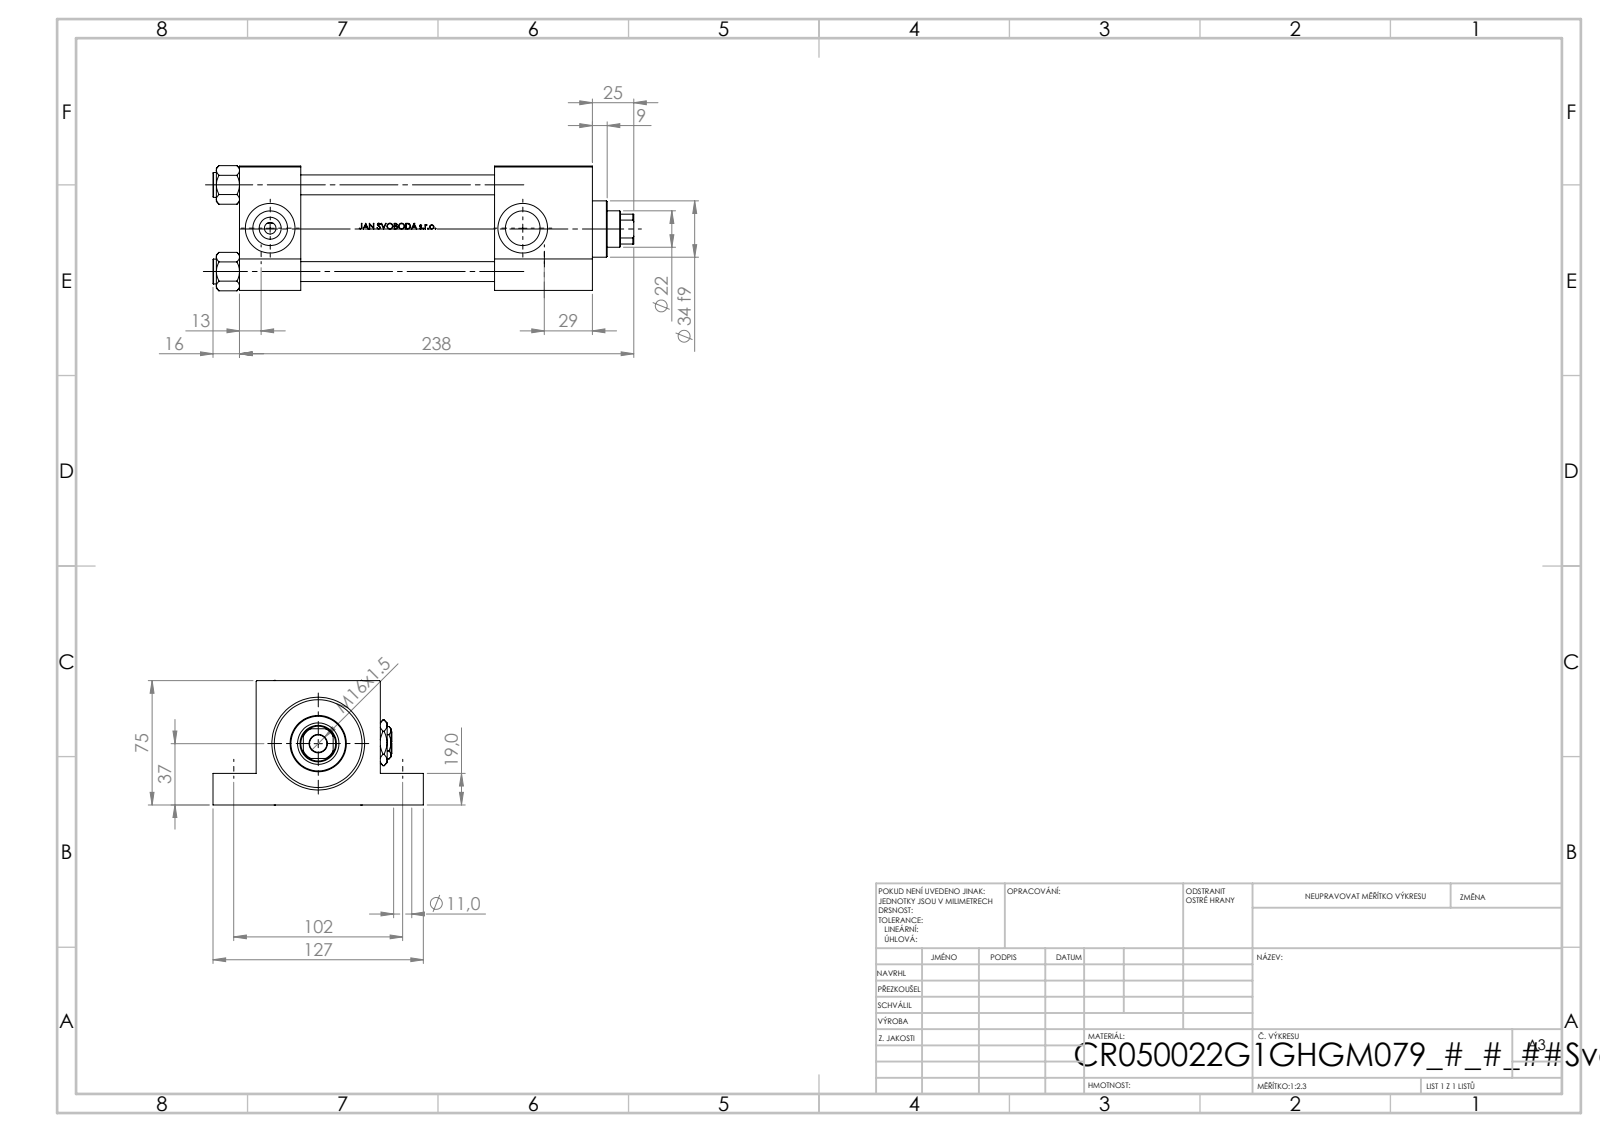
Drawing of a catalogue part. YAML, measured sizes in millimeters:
part_name: "V215CR_VCP_G; V215CR_G_TYCINKA; Zatka_pro_OIL_PORT; V215_VC_A (+2 more)"
step_written_by: "SolidWorks 2019 (CONFIG_CONTROL_DESIGN)"
units: millimeters
bodies: {solids: 12, faces: 1134, planar: 454, cylindrical: 128, other: 552}
overall_size: [254, 127, 75.54]
volume: 830993
surface_area: 193926
round_holes:
  - {diameter: 11, count: 4}
  - {diameter: 12, count: 4}
  - {diameter: 7, count: 2}
  - {diameter: 20.96, count: 2}
  - {diameter: 30, count: 2}
  - {diameter: 10.5, count: 1}
  - {diameter: 22, count: 1}
  - {diameter: 25, count: 1}
  - {diameter: 41, count: 1}
  - {diameter: 50, count: 1}
  - {diameter: 53, count: 1}
round_bosses_or_shafts:
  - {diameter: 15, count: 4}
  - {diameter: 56, count: 1}
  - {diameter: 34, count: 1}
partial_cylinders:
  - {radius: 10.5, count: 1}
face_to_face_distances: [75, 37, 213, 176, 19, 56, 154, 117, 59, 26]
hole_center_spacings: [52.3, 36.63, 37.34, 73.96, 102, 171, 199.11, 152.5]
